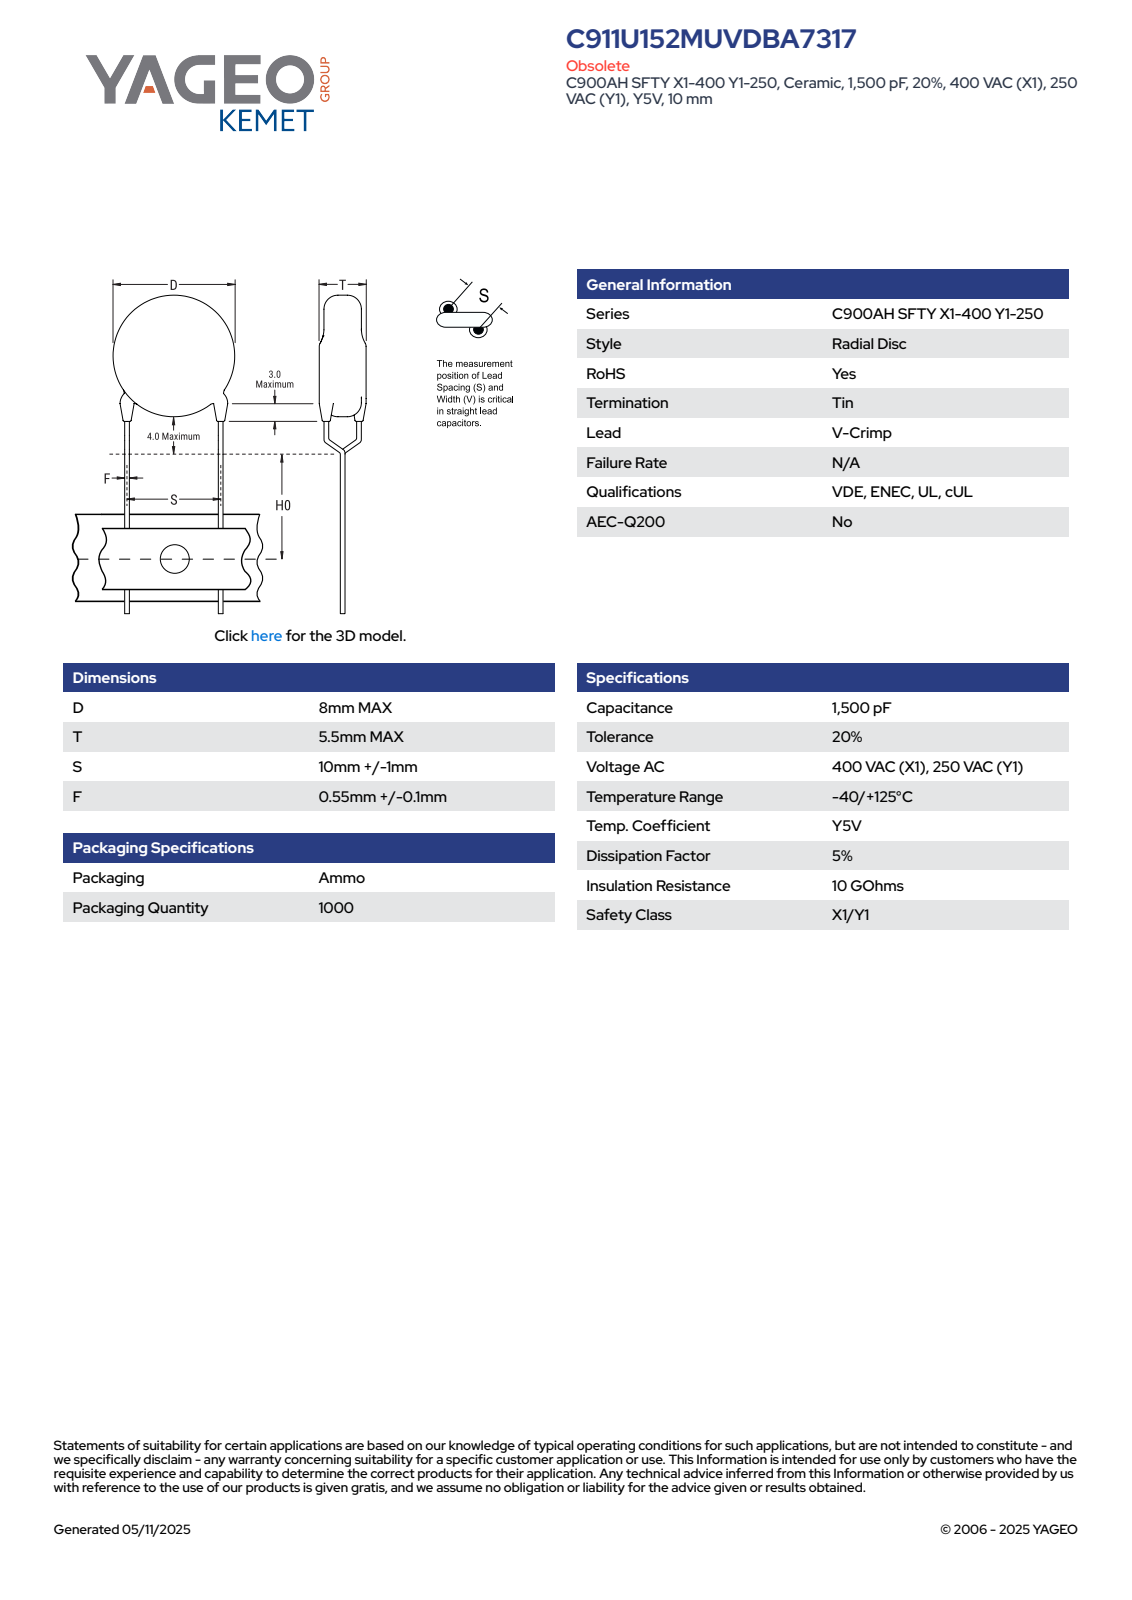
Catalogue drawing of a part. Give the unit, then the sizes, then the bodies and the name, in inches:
Units: inches
Overall size (bounding box): 1.252 × 0.419 × 0.217
Round bosses / shafts (diameter × count): ⌀0.026 ×6, ⌀0.315 ×1
Main face-to-face distances: 0.217, 0.902, 0.041, 1.115, 0.213, 1.074, 0.172, 0.033, 0.018, 0.015
Volume: 0.018 in³ · Surface area: 0.524 in²
Bodies: 5 solids, 93 faces (65 planar, 16 cylindrical, 12 other)
Part name (STEP PRODUCT): CCD_VCC900_D8T5.5S10LL20F0.65
STEP written by: SolidWorks 2014 (AUTOMOTIVE_DESIGN)
